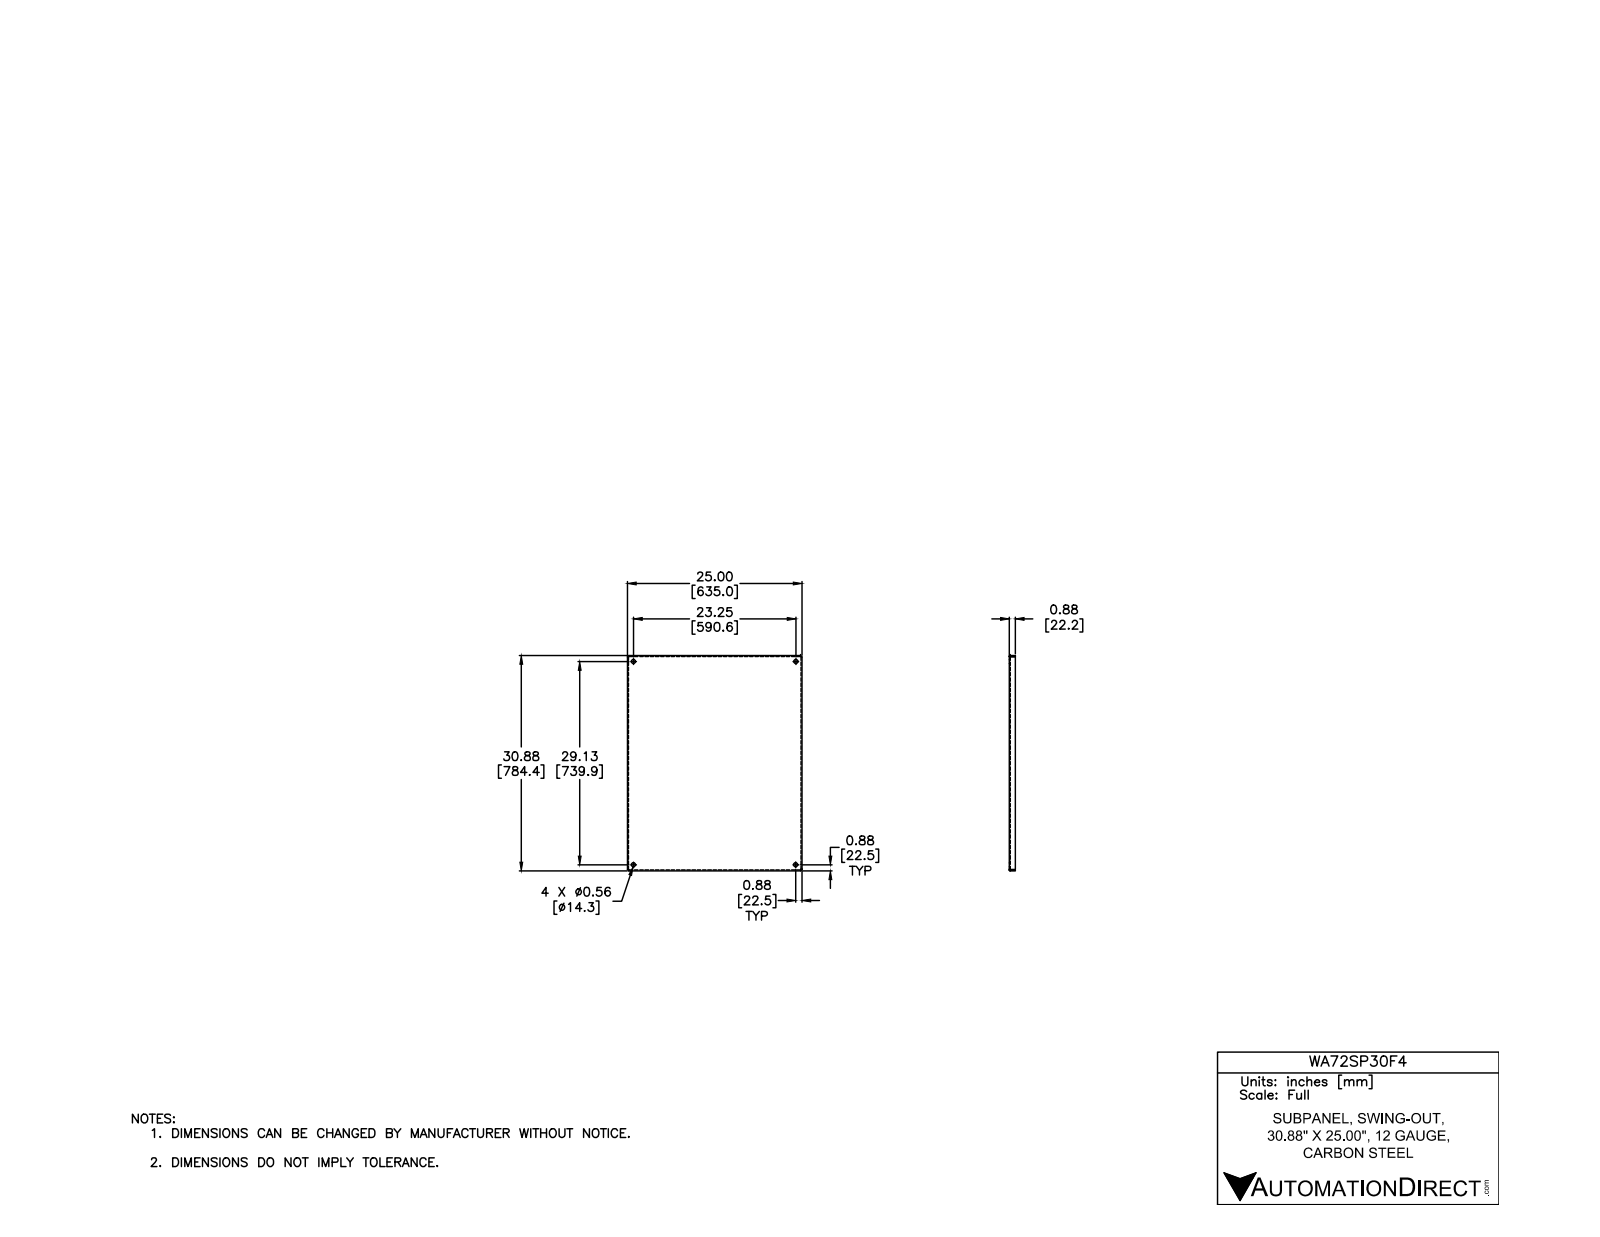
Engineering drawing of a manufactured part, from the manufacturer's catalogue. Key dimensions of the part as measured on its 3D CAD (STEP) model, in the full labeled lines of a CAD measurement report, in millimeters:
Part name (STEP PRODUCT): WA60SP24F3-WA90SP36F4
STEP written by: Autodesk Inventor 2012 (AUTOMOTIVE_DESIGN)
Units: millimetres
Bodies: 1 solid, 42 faces (22 planar, 12 cylindrical, 8 other)
Overall size (bounding box): 784.4 × 635 × 22.2
Volume: 1 311 000 mm³ · Surface area: 1 109 000 mm²
Round holes (diameter × count): ⌀14.3 ×4
Partial cylindrical surfaces — rounded edges, fillets, slot ends (radius × count): R0.8 ×4, R3.2 ×4
Main face-to-face distances: 2.4, 632.6, 782, 635, 630.3, 779.6, 784.4, 19.8, 22.2, 4.1
Hole centre spacings: 590.6, 739.9, 946.7
